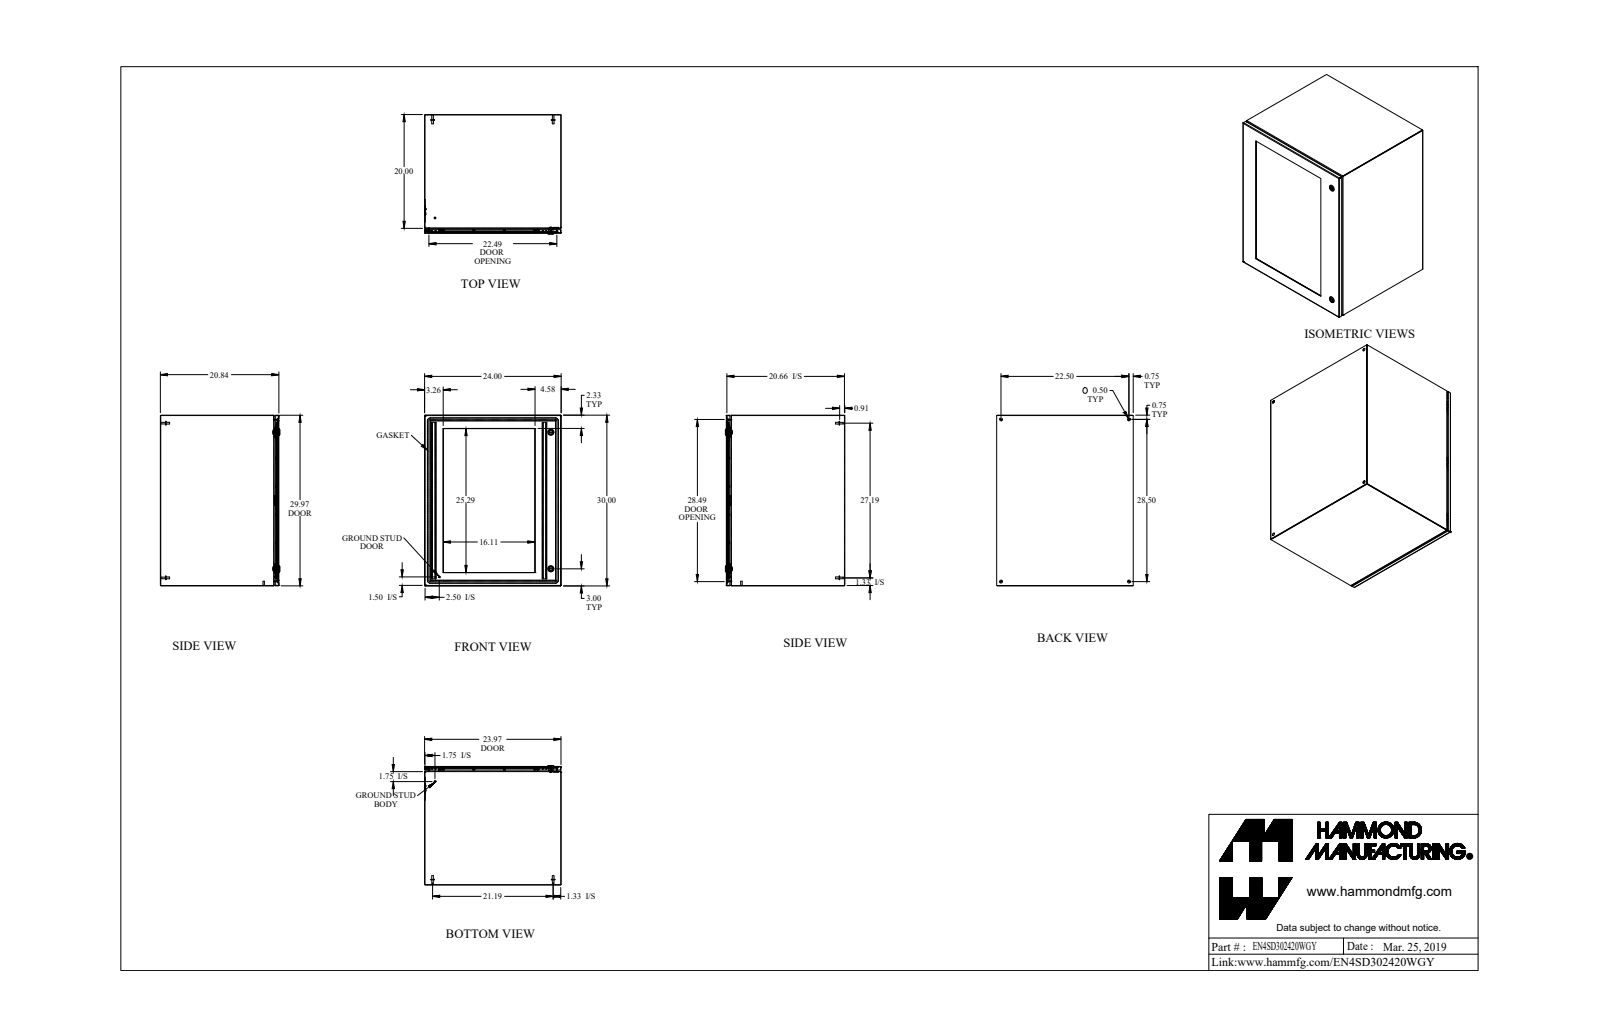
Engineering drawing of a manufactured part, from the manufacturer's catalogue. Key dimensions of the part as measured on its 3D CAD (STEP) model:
Part name (STEP PRODUCT): EN4SD302420WGY
STEP written by: SolidWorks 2019 (AUTOMOTIVE_DESIGN)
Units: inches
Bodies: 82 solids, 1605 faces (810 planar, 499 cylindrical, 296 other)
Overall size (bounding box): 30 × 24 × 20.997
Volume: 374.1 in³ · Surface area: 8 417 in²
Round holes (diameter × count): ⌀0.13 ×20, ⌀0.25 ×20, ⌀0.5 ×4, ⌀0.232 ×2, ⌀0.625 ×2, ⌀0.785 ×2, ⌀0.172 ×1, ⌀0.24 ×1, ⌀0.242 ×1
Round bosses / shafts (diameter × count): ⌀0.226 ×21, ⌀0.368 ×20, ⌀0.164 ×20, ⌀0.625 ×4, ⌀0.313 ×4, ⌀0.27 ×4, ⌀1.1 ×2, ⌀0.525 ×2
Partial cylindrical surfaces — rounded edges, fillets, slot ends (radius × count): R0.036 ×14, R0.108 ×14, R0.043 ×12, R0.081 ×12, R0.125 ×12, R0.312 ×12, R0.1 ×8, R0.006 ×6
Main face-to-face distances: 0.072, 23.928, 20.765, 29.928, 20.693, 23.856, 24, 20.443, 0.25, 20.515
Hole centre spacings: 9.95, 19.822, 4.975, 5.372, 16.645, 17.144, 17.852, 26.874
